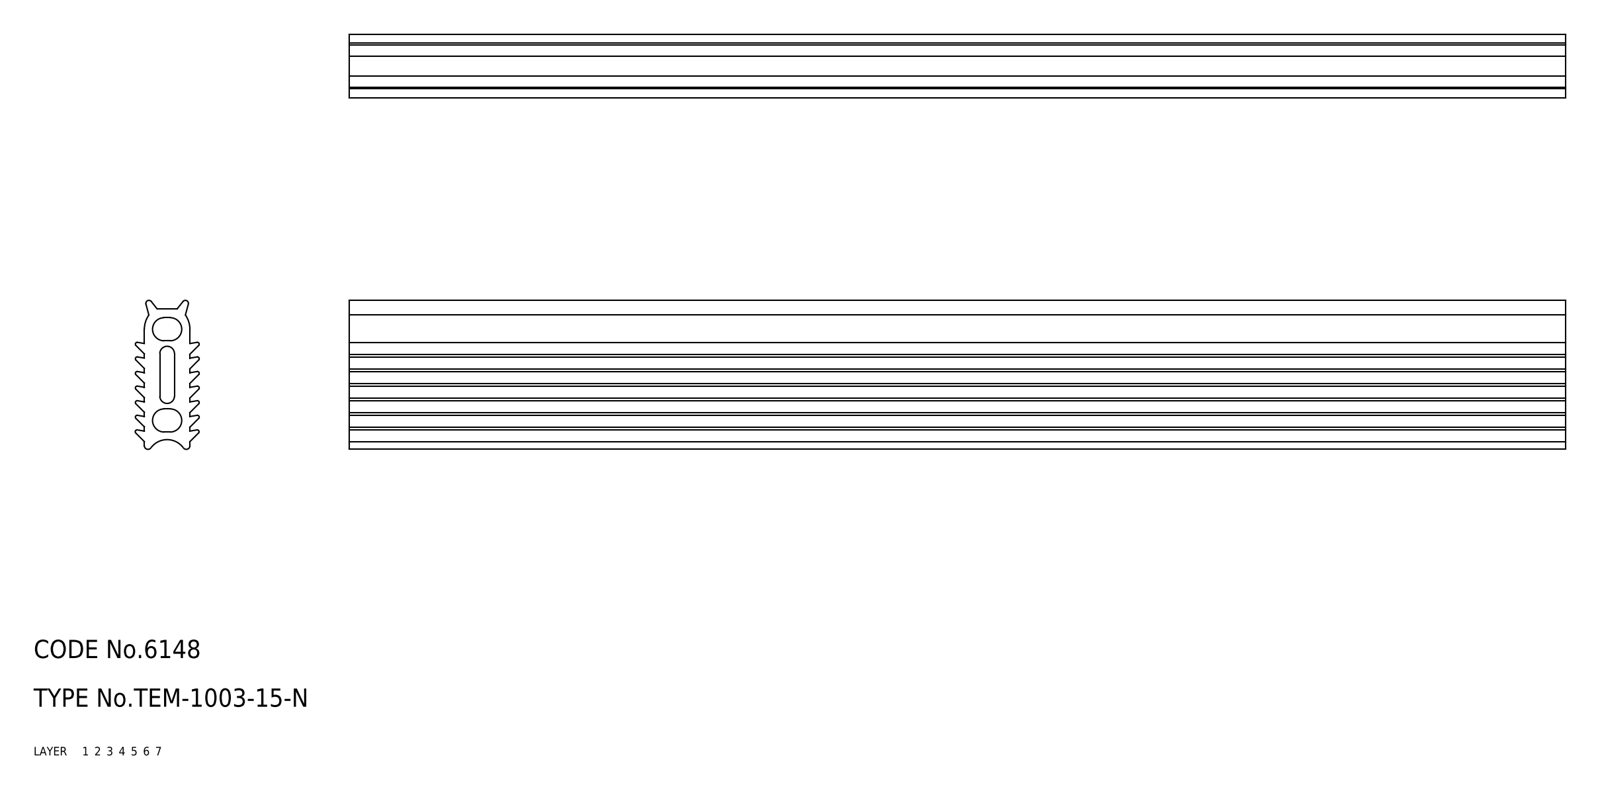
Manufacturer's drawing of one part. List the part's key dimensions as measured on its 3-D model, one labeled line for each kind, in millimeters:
Part name (STEP PRODUCT): gasket
STEP written by: CADfix (AUTOMOTIVE_DESIGN)
Units: millimetres
Bodies: 1 solid, 84 faces (0 planar, 0 cylindrical, 84 other)
Overall size (bounding box): 200 × 24.5 × 10.53
Volume: 27 746 mm³ · Surface area: 29 373 mm²
